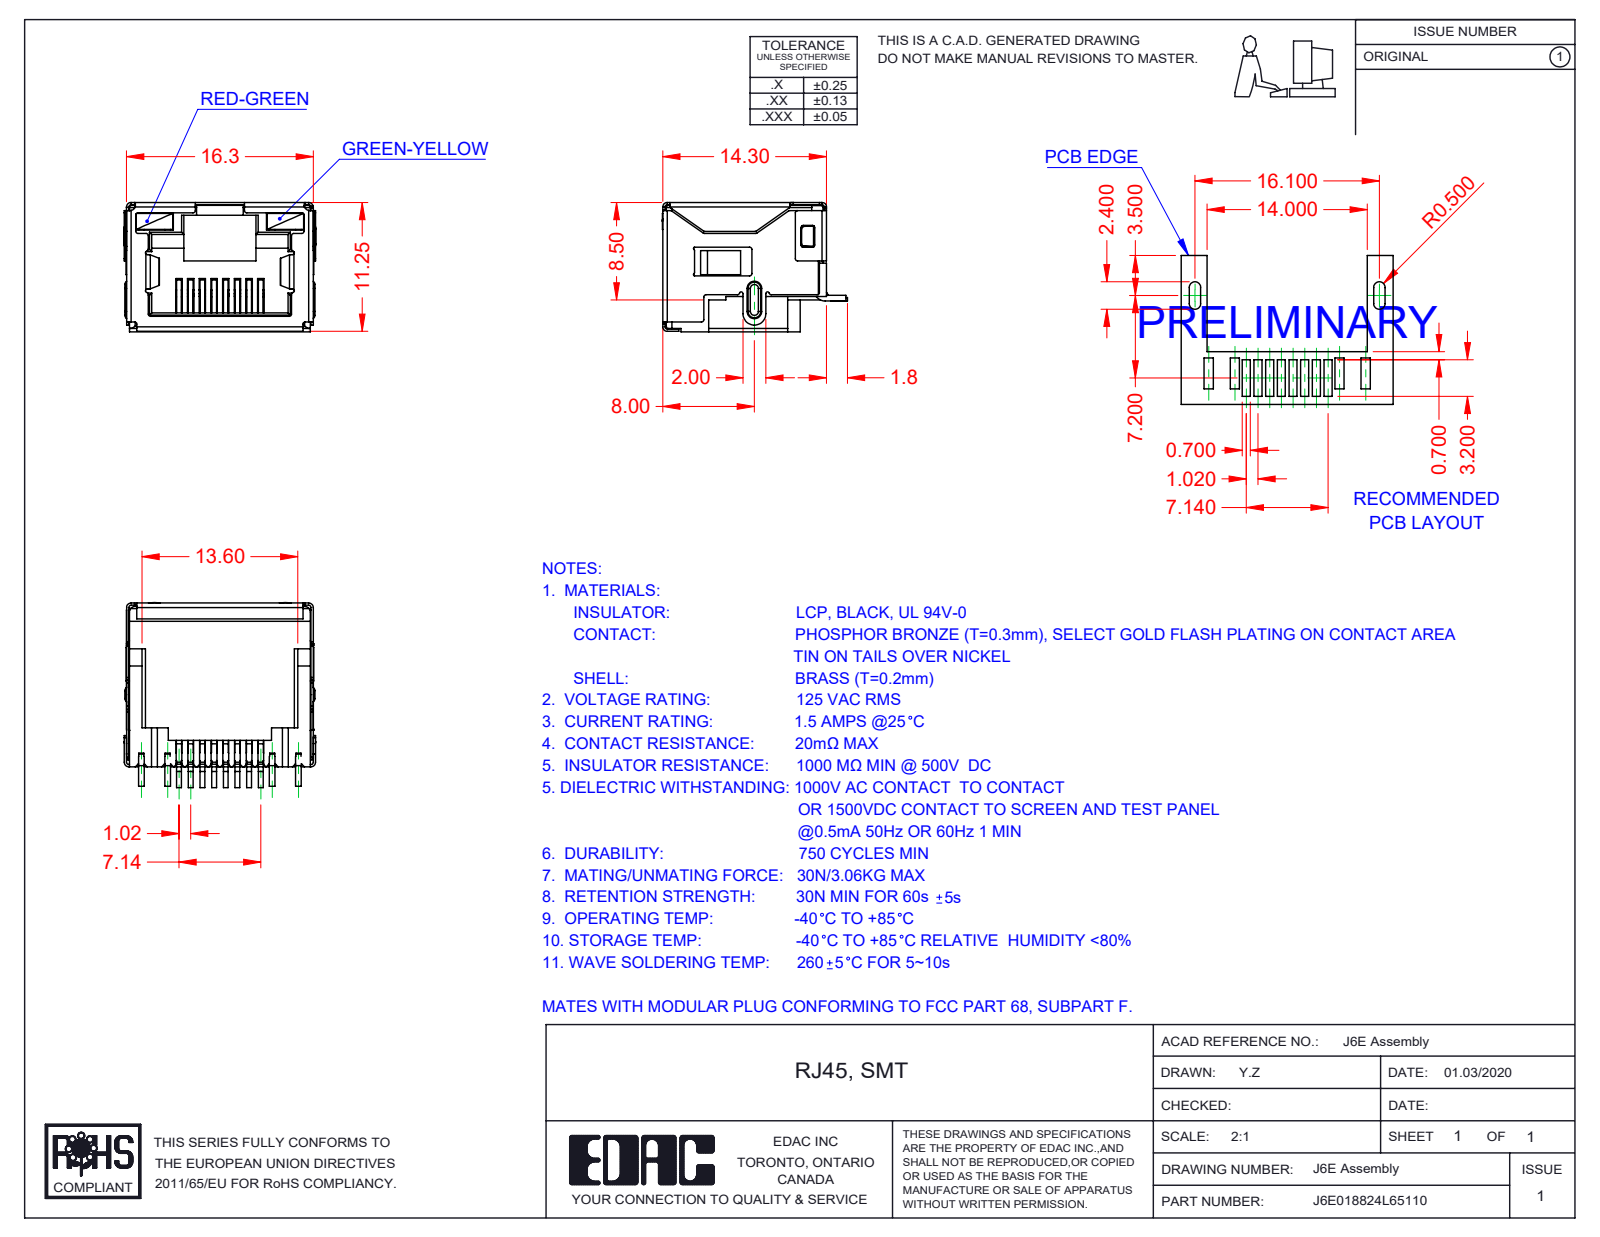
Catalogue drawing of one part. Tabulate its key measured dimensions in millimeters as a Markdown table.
| quantity | value |
| --- | --- |
| part name | 6E LED LH_6-Red-Green; 6E Shield_LED; J6E018824L65110; 6E Contacts (+2 more) |
| STEP written by | SolidWorks 2016 (CONFIG_CONTROL_DESIGN) |
| units | millimeters |
| bodies | 12 solids, 1500 faces (1099 planar, 351 cylindrical, 50 other) |
| overall size | 16.75 × 16.15 × 11.3 |
| volume | 1 109 mm³ |
| surface area | 4 045 mm² |
| partial cylindrical surfaces (radius × count) | 0.2 × 82, 0.25 × 17, 0.4 × 13, 0.5 × 13, 0.1 × 10, 0.15 × 7, 0.3 × 4, 1 × 3 |
| main face-to-face distances | 11.05, 16.05, 16.1, 15.85, 11.1, 11.3, 2.4, 0.7, 9.85, 0.49 |
